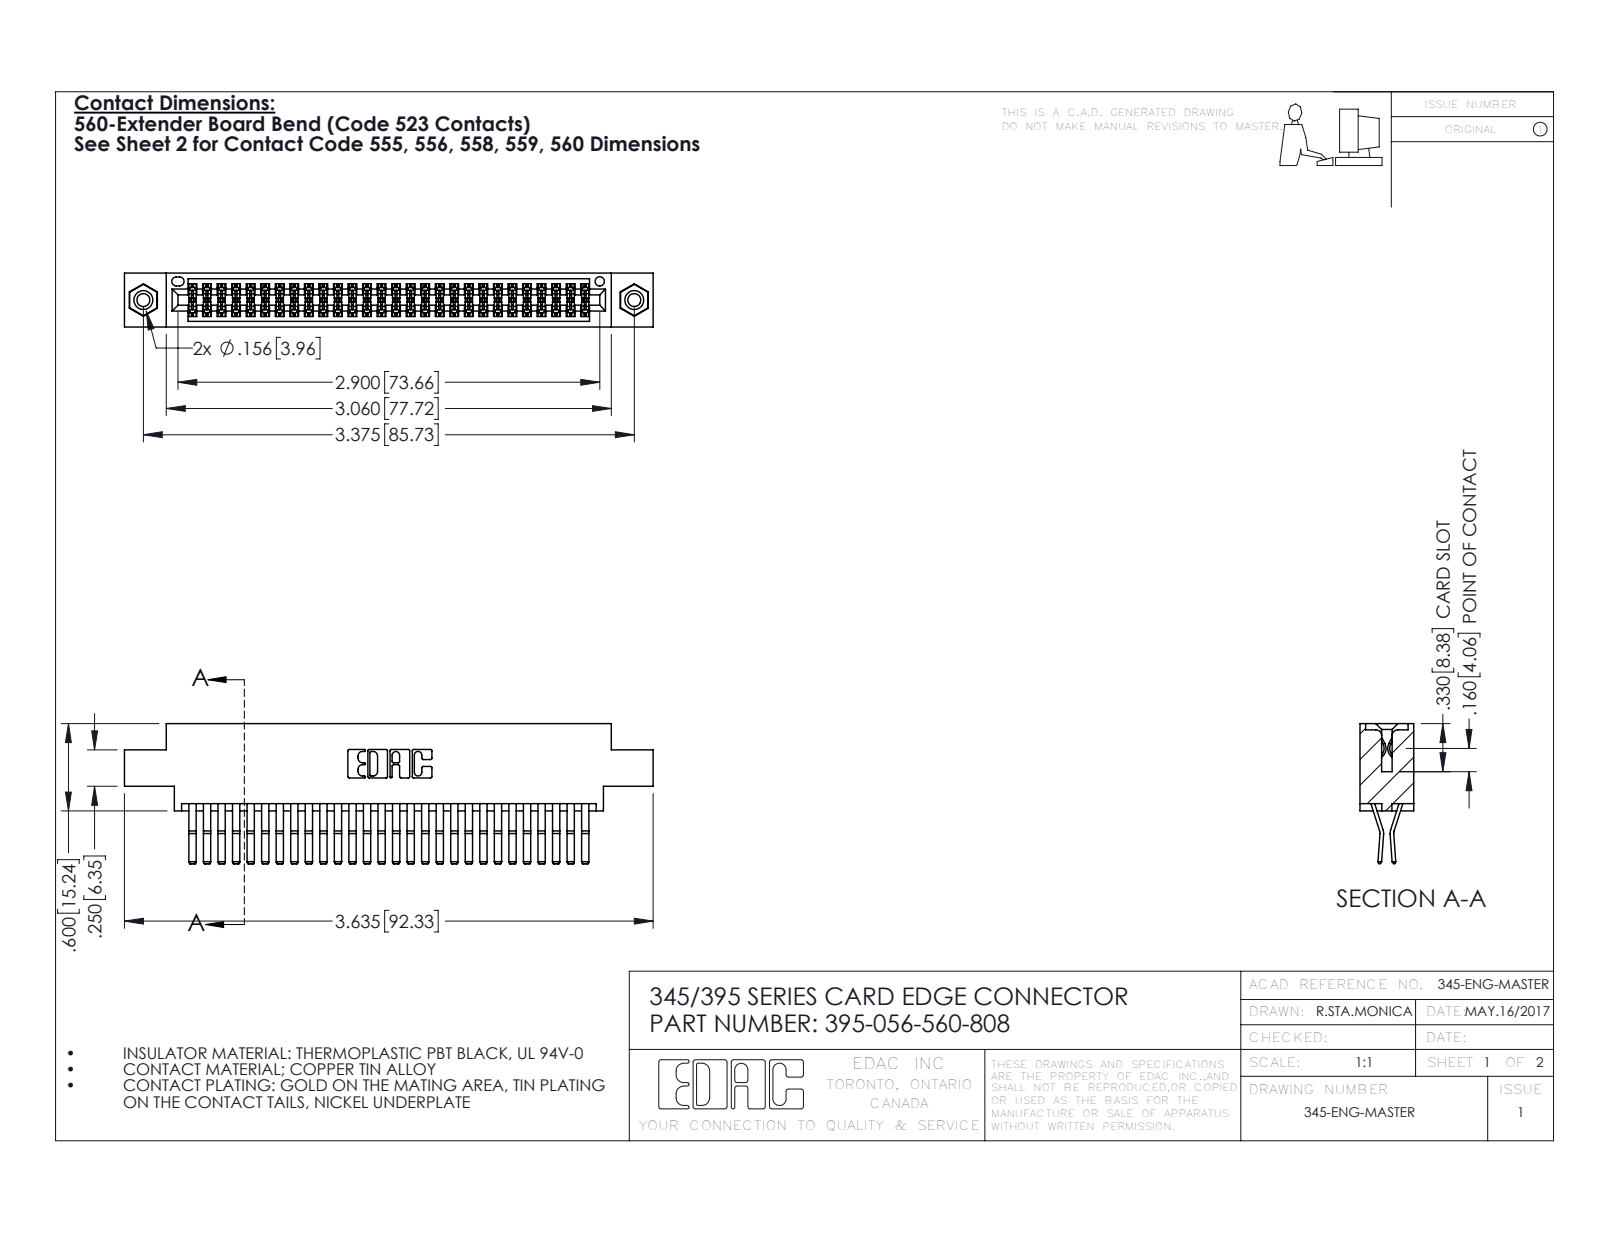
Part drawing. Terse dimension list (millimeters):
name: 345-292-001_560 Tail; 345 Part_0.170 Offset - 0.156 Dia-TI; 345-250-001_345-250-003-102; 395-056-560-808
written by: SolidWorks 2016 (CONFIG_CONTROL_DESIGN)
unit: mm
bodies: 59 solids, 3102 faces (1964 planar, 1122 cylindrical, 16 other)
size: 92.3 × 24.4 × 9.4
volume: 9 080 mm³; area: 14 260 mm²
holes: 2× ⌀2.3, 2× ⌀3.2, 2× ⌀4, 1× ⌀1.6
bosses: 2× ⌀3.9
rounds: 111× R0.2, 22× R0.3, 6× R0.2, 6× R0.8, 3× R0.7, 2× R0.3, 2× R0.4, 2× R0.5
face distances: 0.6, 1.8, 7.6, 9.4, 5.1, 2.5, 6.9, 5.7, 4.4, 3.8
hole spacings: 6.9, 79.8, 85.7
